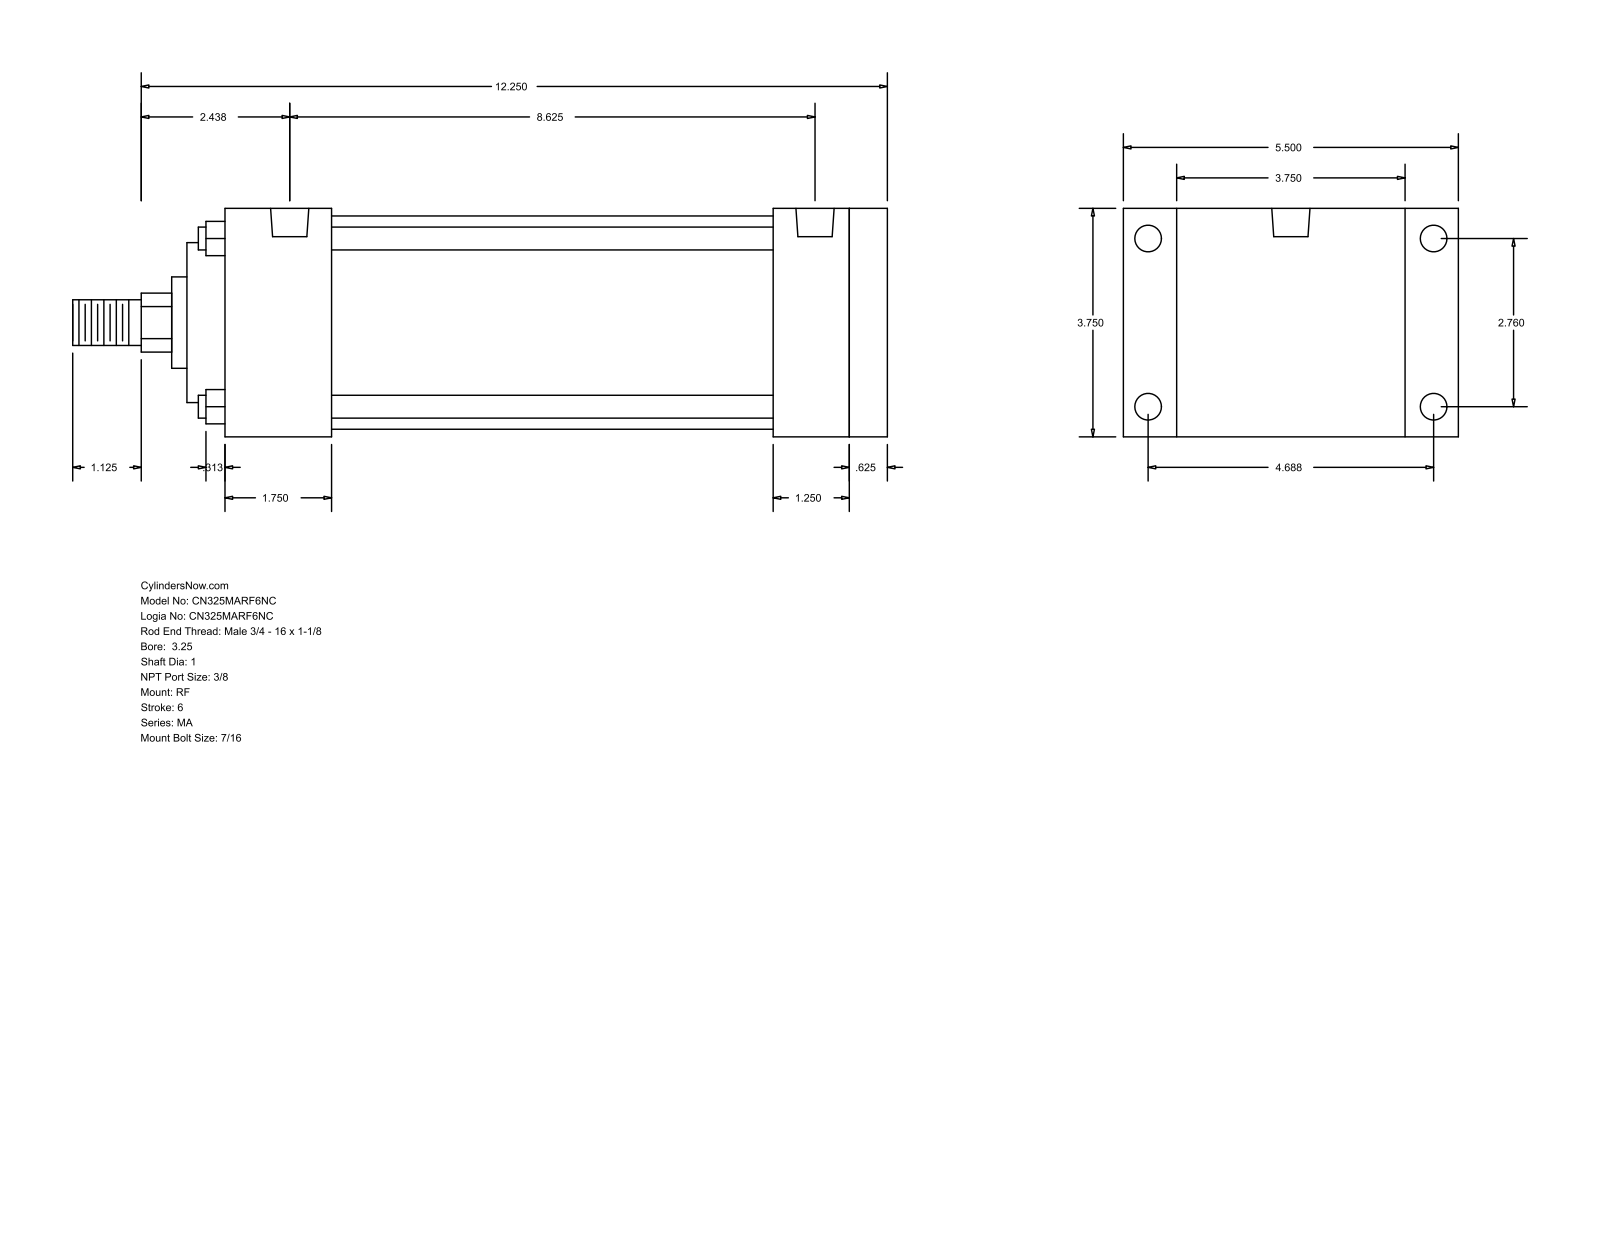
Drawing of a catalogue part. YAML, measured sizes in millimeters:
part_name: "MA_RF__0325_1"
step_written_by: "GSSL Pune (CONFIG_CONTROL_DESIGN)"
units: millimeters
bodies: {solids: 0, faces: 94, planar: 65, cylindrical: 29, other: 0}
overall_size: [339.73, 139.7, 95.25]
round_holes:
  - {diameter: 11.11, count: 8}
  - {diameter: 15.93, count: 2}
round_bosses_or_shafts:
  - {diameter: 9.53, count: 4}
  - {diameter: 88.9, count: 1}
  - {diameter: 66.67, count: 1}
  - {diameter: 38.1, count: 1}
  - {diameter: 25.4, count: 1}
  - {diameter: 19.05, count: 1}
partial_cylinders:
  - {radius: 12.29, count: 1}
face_to_face_distances: [95.24, 276.23, 260.35, 15.88, 22.23, 117.47, 228.6, 31.75, 47.63, 44.46]
hole_center_spacings: [4.76, 70.1, 119.06, 138.16, 209.56, 214.32, 219.08]
